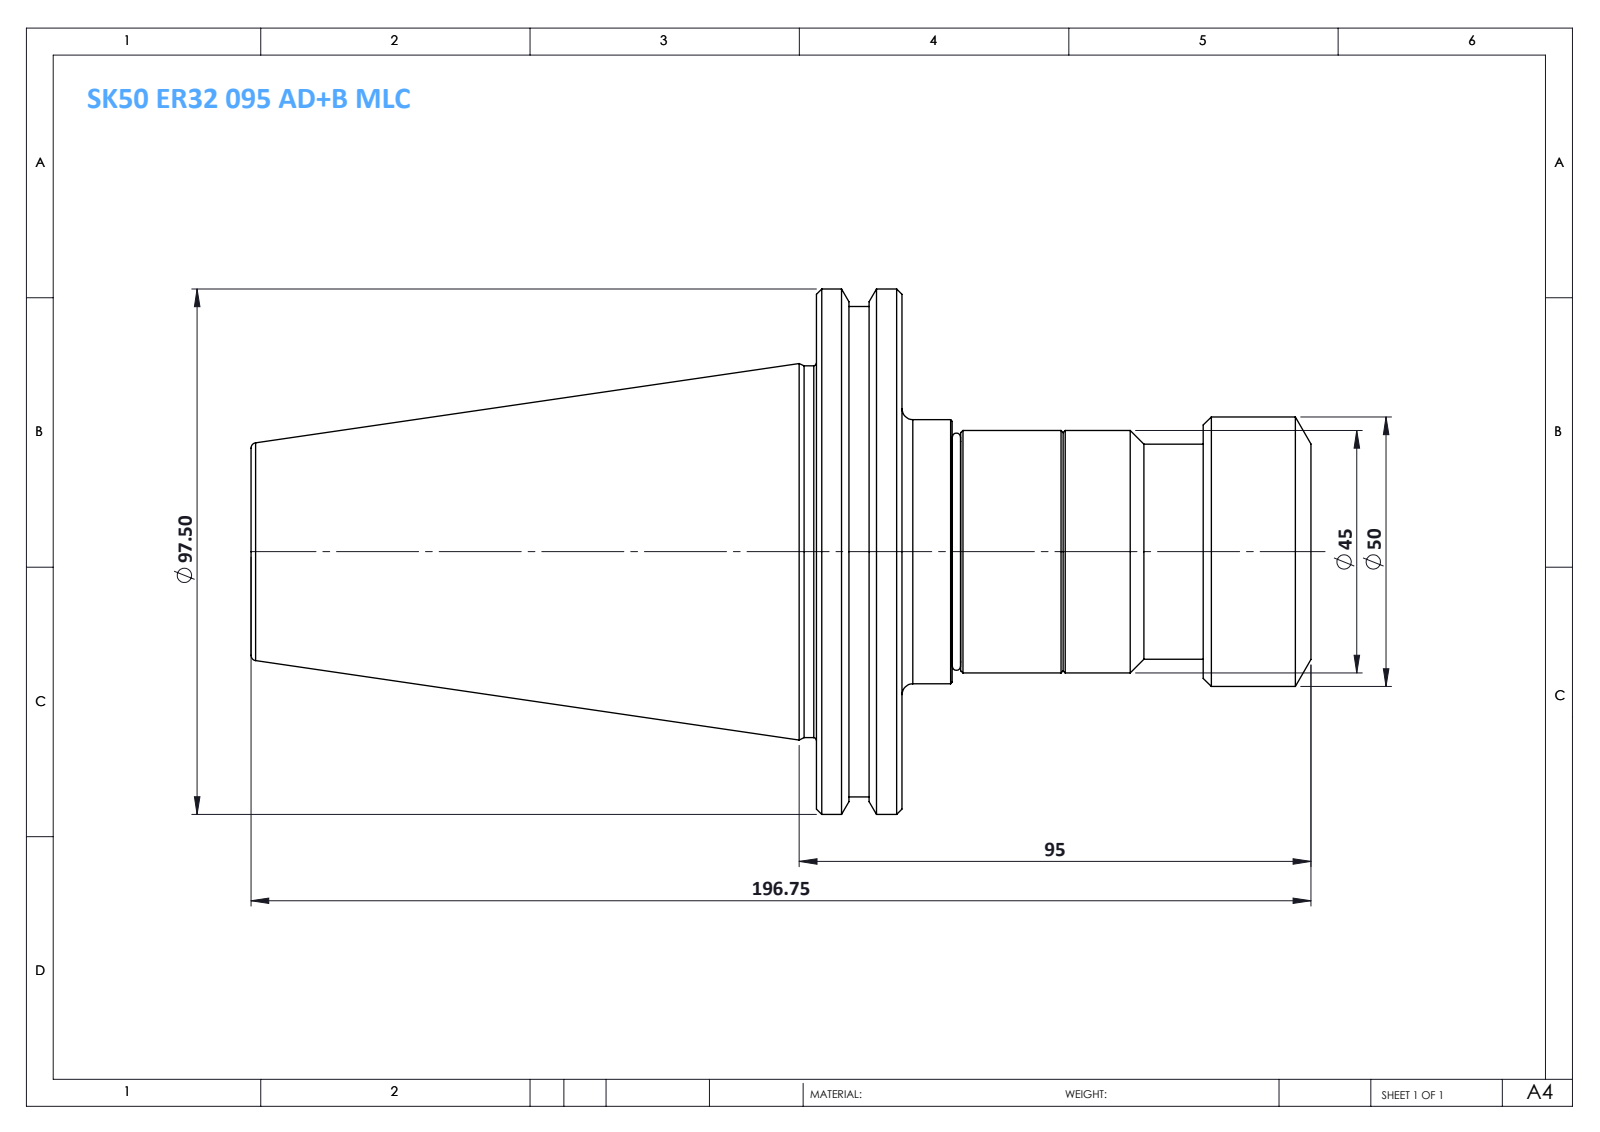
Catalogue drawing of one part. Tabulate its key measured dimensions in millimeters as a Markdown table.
| quantity | value |
| --- | --- |
| part name | SK 50 ER 32 095 AD+B MLC (1) |
| STEP written by | SolidWorks 2014 (CONFIG_CONTROL_DESIGN) |
| units | millimeters |
| bodies | 2 solids, 65 faces (9 planar, 20 cylindrical, 36 other) |
| overall size | 196.75 × 97.5 × 97.5 |
| volume | 498 944 mm³ |
| surface area | 49 329 mm² |
| round bosses / shafts (diameter × count) | 97.5 × 1, 91 × 1, 69 × 1, 50 × 1, 49 × 1, 45 × 1, 40.9 × 1, 39.9 × 1 |
| main face-to-face distances | 15.9, 75.9, 91.8, 196.75, 120.85, 104.95, 66.6, 9.3, 25.2, 130.15 |
